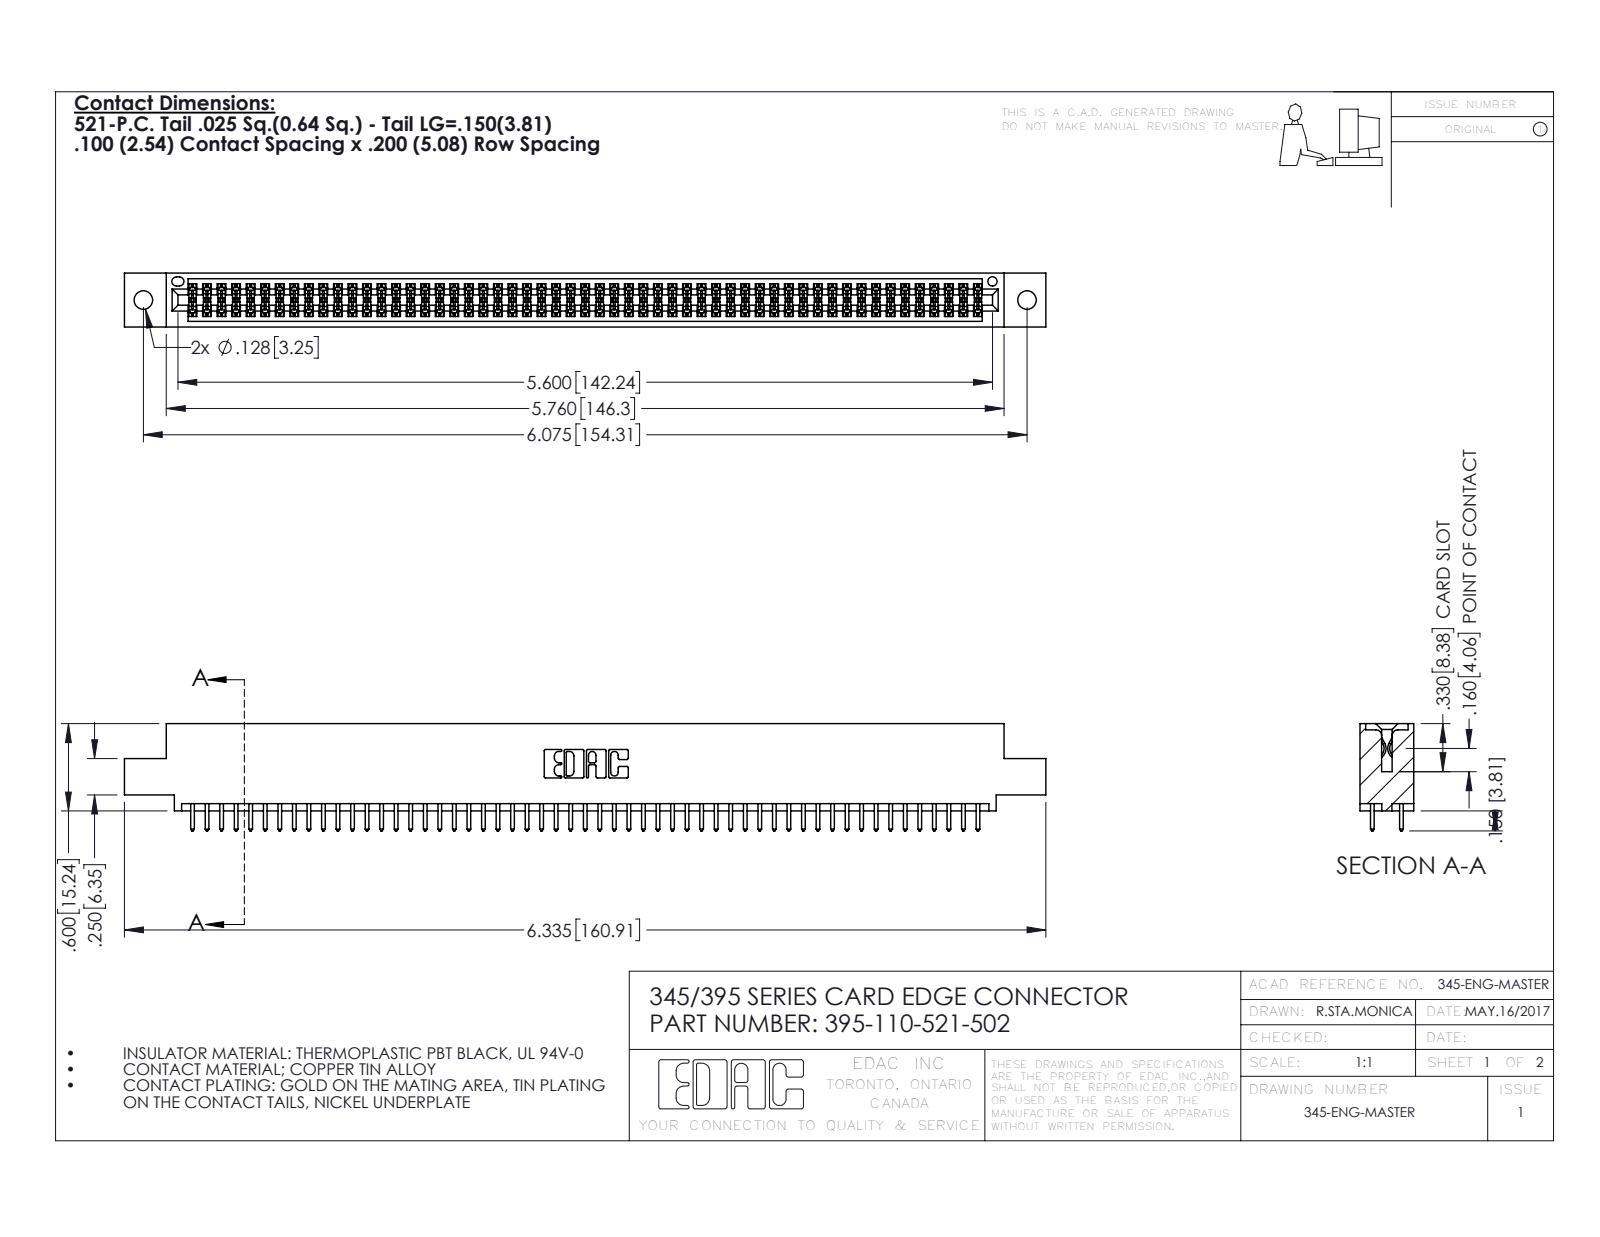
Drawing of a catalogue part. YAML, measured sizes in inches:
part_name: "345 Part_0.110 Offset - 0.128 Dia; 395-110-521-502; 345-292-001_345-293-121"
step_written_by: "SolidWorks 2016 (CONFIG_CONTROL_DESIGN)"
units: inches
bodies: {solids: 111, faces: 5630, planar: 3714, cylindrical: 1916, other: 0}
overall_size: [6.335, 0.737, 0.37]
volume: 0.952
surface_area: 35.39
round_holes:
  - {diameter: 0.128, count: 2}
  - {diameter: 0.064, count: 1}
partial_cylinders:
  - {radius: 0.006, count: 165}
  - {radius: 0.01, count: 110}
  - {radius: 0.01, count: 22}
  - {radius: 0.007, count: 6}
  - {radius: 0.031, count: 6}
  - {radius: 0.026, count: 3}
  - {radius: 0.014, count: 2}
  - {radius: 0.019, count: 2}
face_to_face_distances: [0.072, 0.298, 0.2, 0.098, 0.272, 0.025, 0.37, 0.225, 0.175, 0.149]
hole_center_spacings: [0.27, 5.839, 6.075]
